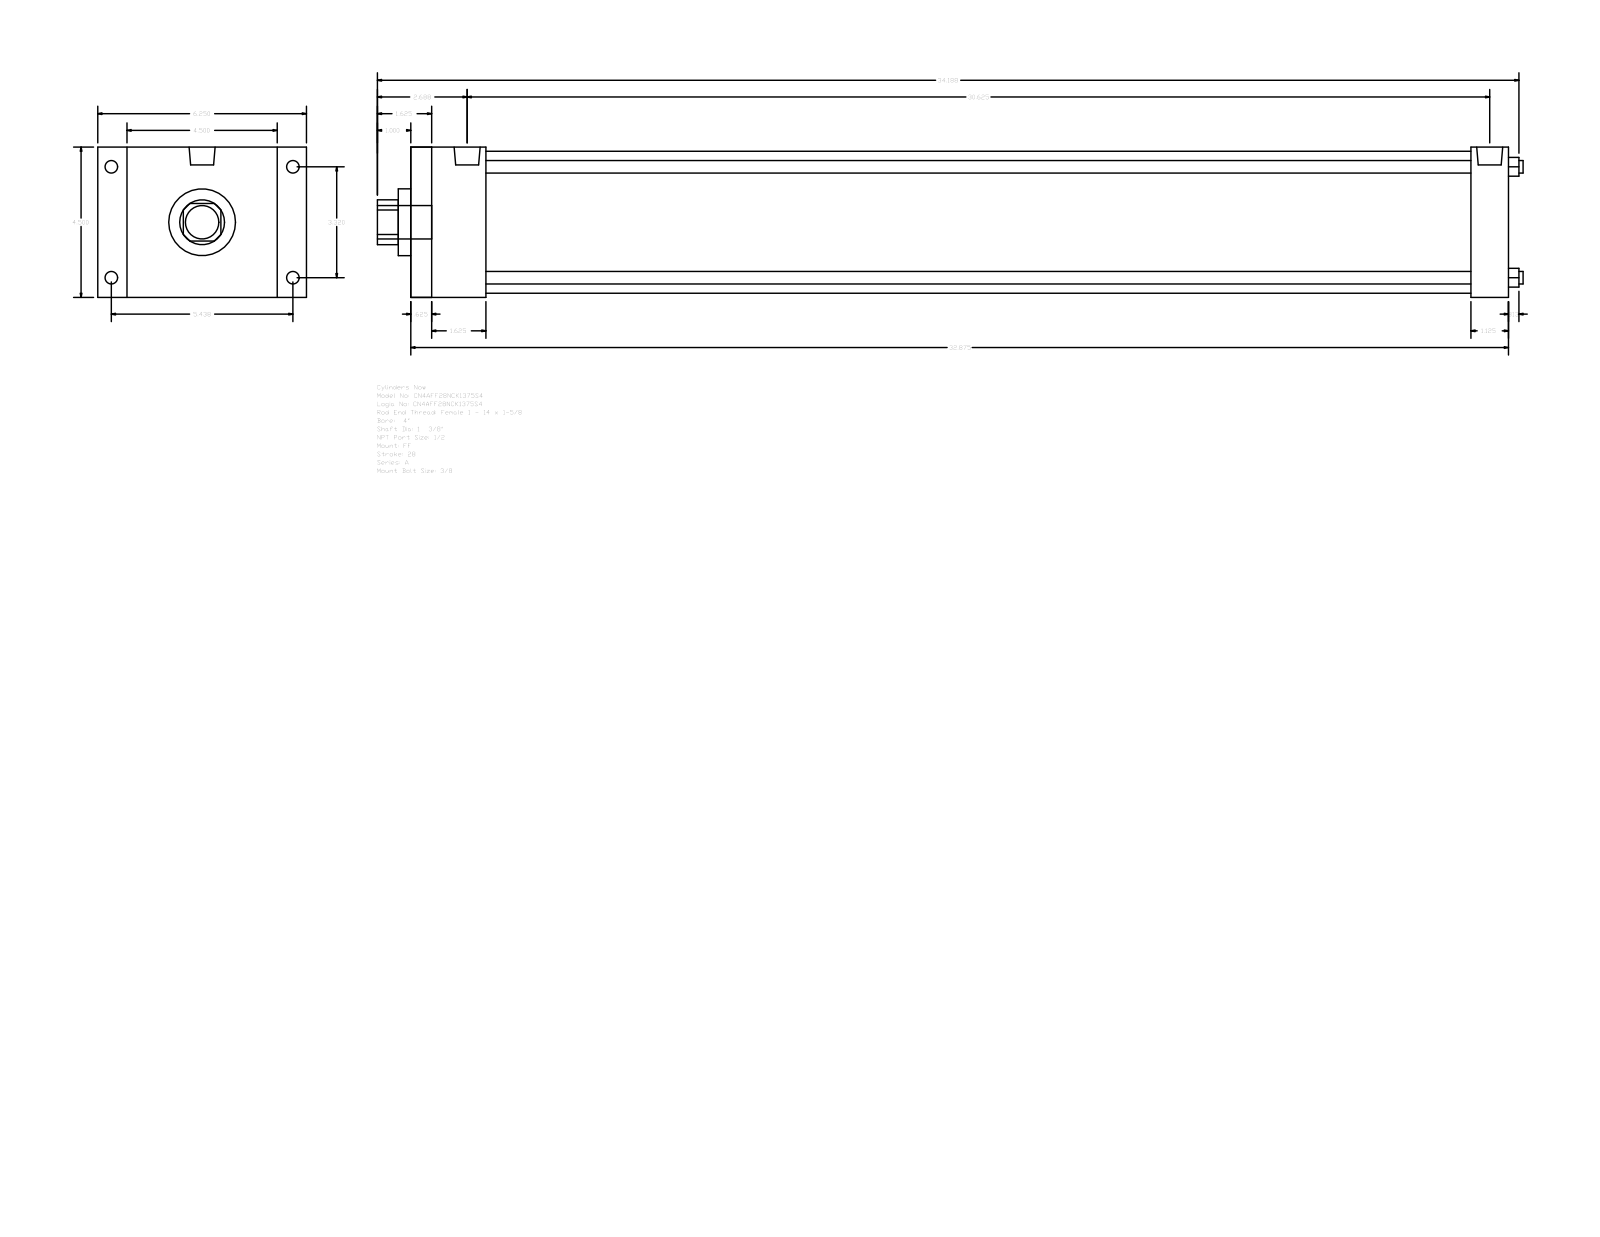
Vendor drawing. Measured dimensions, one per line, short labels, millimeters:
name: A_FF__0400_1.375
written by: GSSL Pune (CONFIG_CONTROL_DESIGN)
unit: mm
bodies: 0 solids, 92 faces (64 planar, 28 cylindrical, 0 other)
size: 871.54 × 158.75 × 114.3
holes: 4× ⌀9.53, 1× ⌀34.92, 1× ⌀50.8, 1× ⌀107.95
bosses: 4× ⌀9.53, 4× ⌀8.73, 2× ⌀19.77, 1× ⌀25.4
rounds: 1× R17.06
face distances: 114.3, 835.02, 819.15, 15.87, 28.57, 22.23, 136.53, 806.45, 790.58, 57.15
hole spacings: 59.62, 84.32, 119.25
